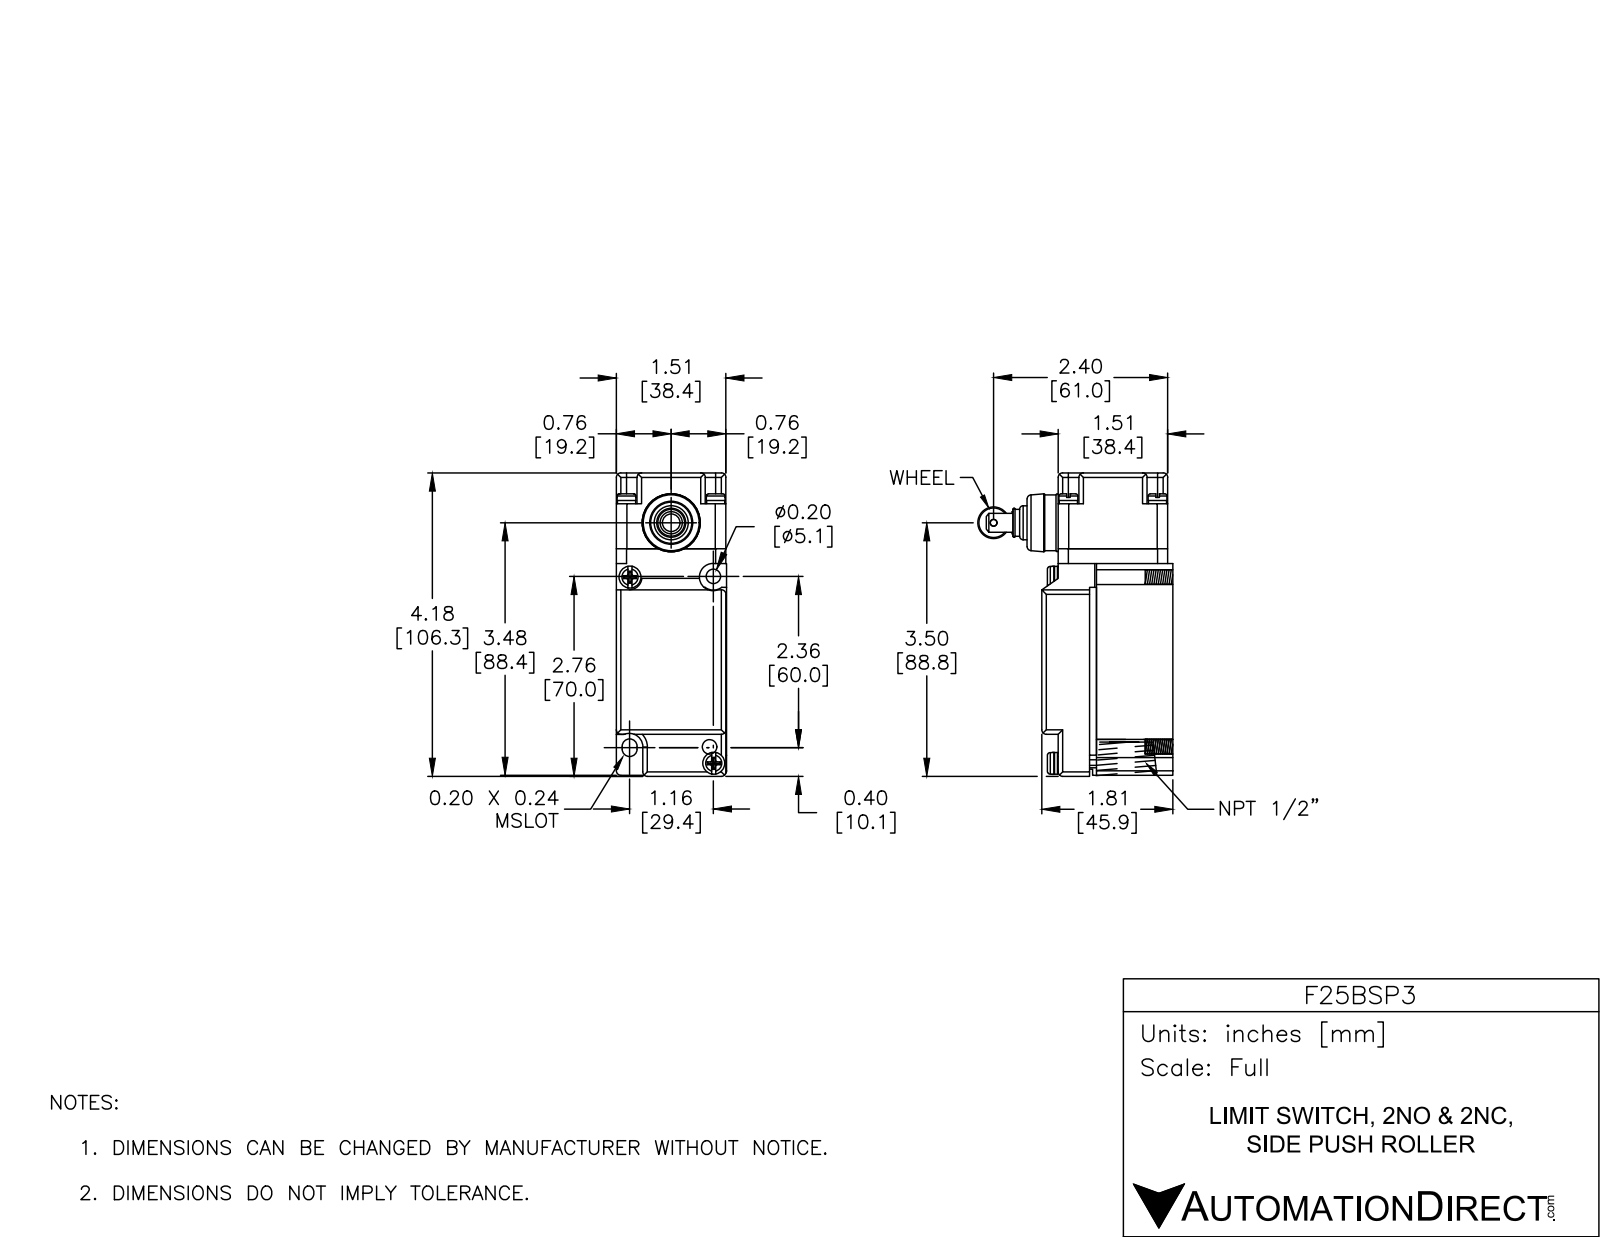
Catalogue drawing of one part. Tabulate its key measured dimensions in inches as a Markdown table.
| quantity | value |
| --- | --- |
| part name | Imported29; Imported28; Imported27; Imported33 (+8 more) |
| STEP written by | SolidWorks 2002296 (CONFIG_CONTROL_DESIGN) |
| units | inches |
| bodies | 14 solids, 633 faces (237 planar, 178 cylindrical, 218 other) |
| overall size | 4.184 × 2.692 × 1.52 |
| volume | 10.24 in³ |
| surface area | 71.16 in² |
| round holes (diameter × count) | 0.177 × 4, 0.19 × 3, 0.2 × 3, 0.094 × 1, 0.13 × 1, 0.23 × 1, 0.232 × 1, 0.26 × 1, 0.419 × 1, 0.58 × 1, 0.63 × 1, 0.72 × 1 |
| round bosses / shafts (diameter × count) | 0.26 × 4, 0.25 × 4, 0.14 × 4, 0.302 × 2, 0.3 × 2, 0.77 × 1, 0.655 × 1, 0.565 × 1 |
| partial cylindrical surfaces (radius × count) | 0.062 × 29, 0.03 × 16, 0.015 × 8, 0.145 × 8, 0.14 × 4, 0.102 × 2, 0.188 × 2, 0.19 × 2 |
| main face-to-face distances | 0.094, 1.149, 1.055, 1.52, 0.66, 0.754, 1.809, 1.51, 0.227, 0.433 |
| hole center spacings | 1.23, 1.23, 1.74, 2.815, 0.225, 0.235, 0.936, 0.942 |
